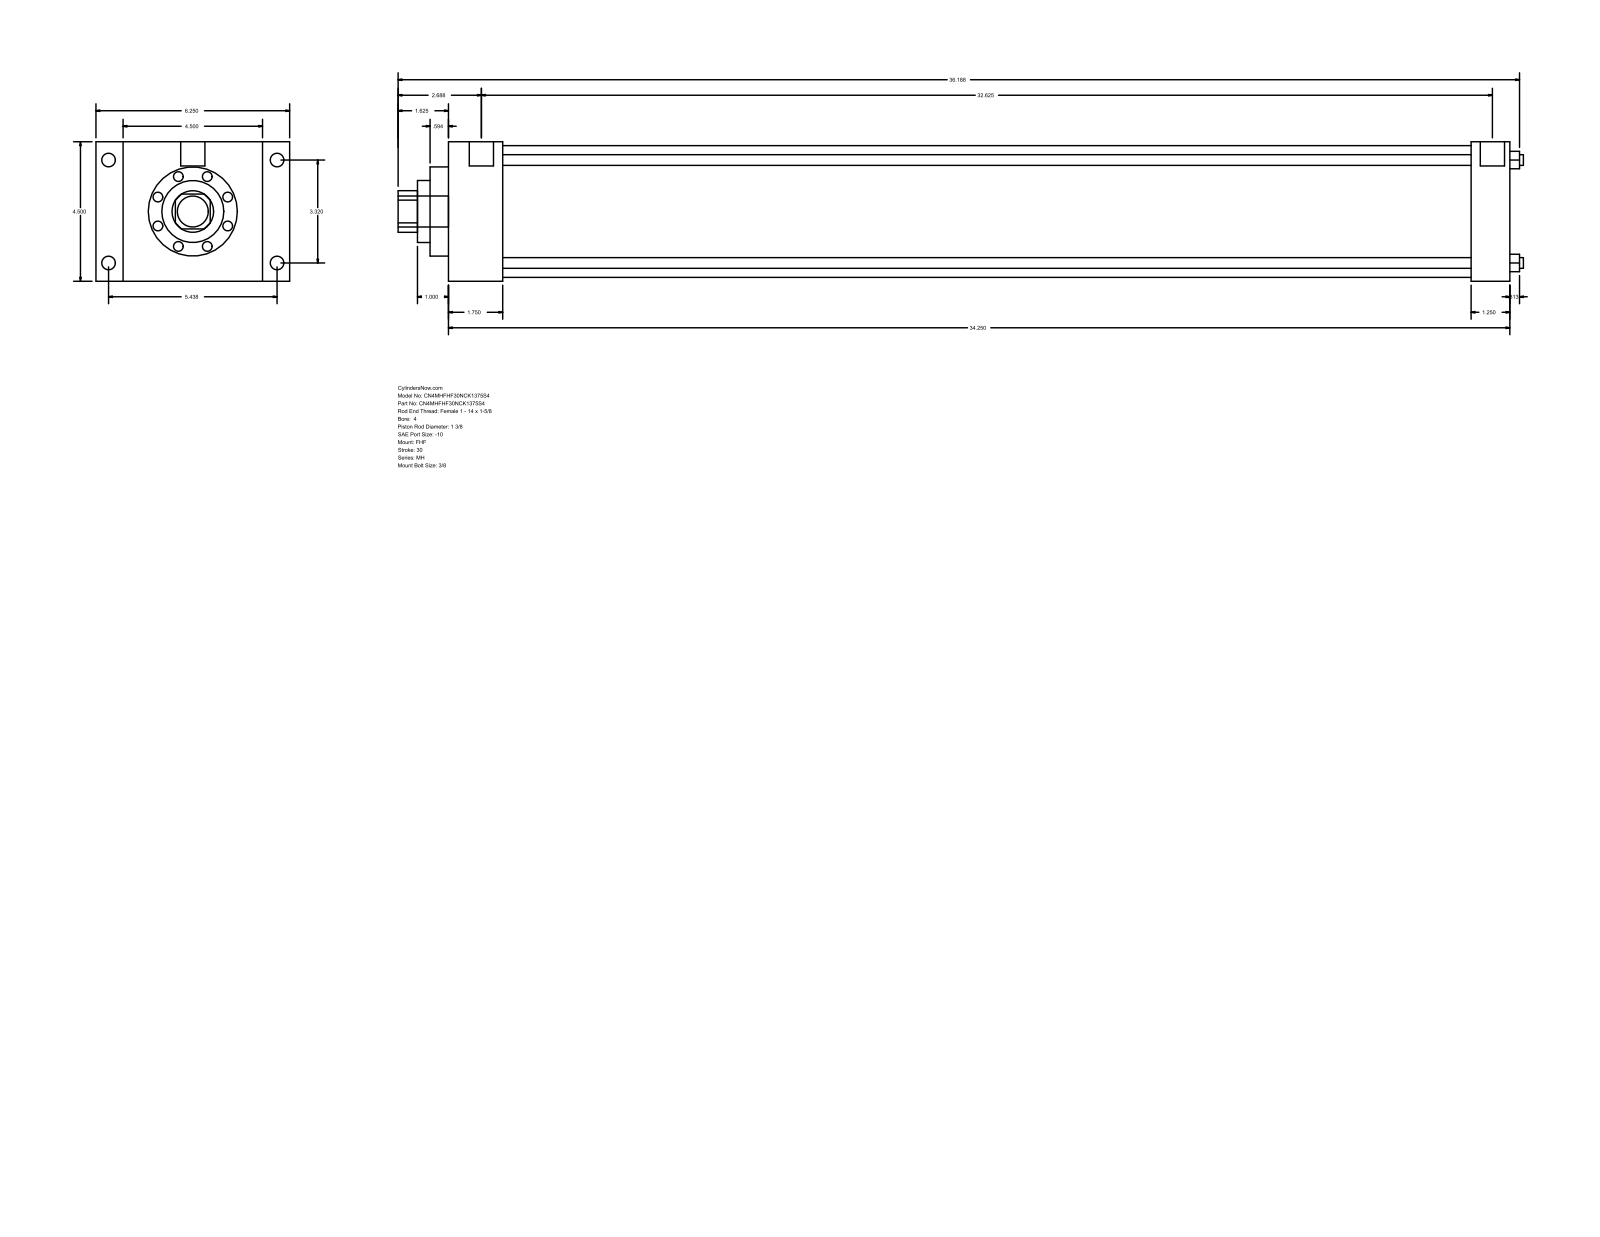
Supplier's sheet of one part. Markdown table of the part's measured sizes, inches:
| quantity | value |
| --- | --- |
| part name | MH_FHF__0400_1.375 |
| STEP written by | GSSL Pune (CONFIG_CONTROL_DESIGN) |
| units | inches |
| bodies | 0 solids, 90 faces (61 planar, 29 cylindrical, 0 other) |
| overall size | 36.313 × 6.25 × 4.5 |
| round holes (diameter × count) | 0.345 × 4, 1.375 × 1, 2 × 1, 2.875 × 1, 4.25 × 1 |
| round bosses / shafts (diameter × count) | 0.438 × 4, 0.344 × 4, 0.781 × 2, 1 × 1 |
| partial cylindrical surfaces (radius × count) | 0.672 × 1 |
| main face-to-face distances | 4.5, 34.25, 1.75, 32.5, 0.875, 5.375, 6.25, 33, 31.25, 1.25 |
| hole center spacings | 2.347, 3.32, 4.695 |
